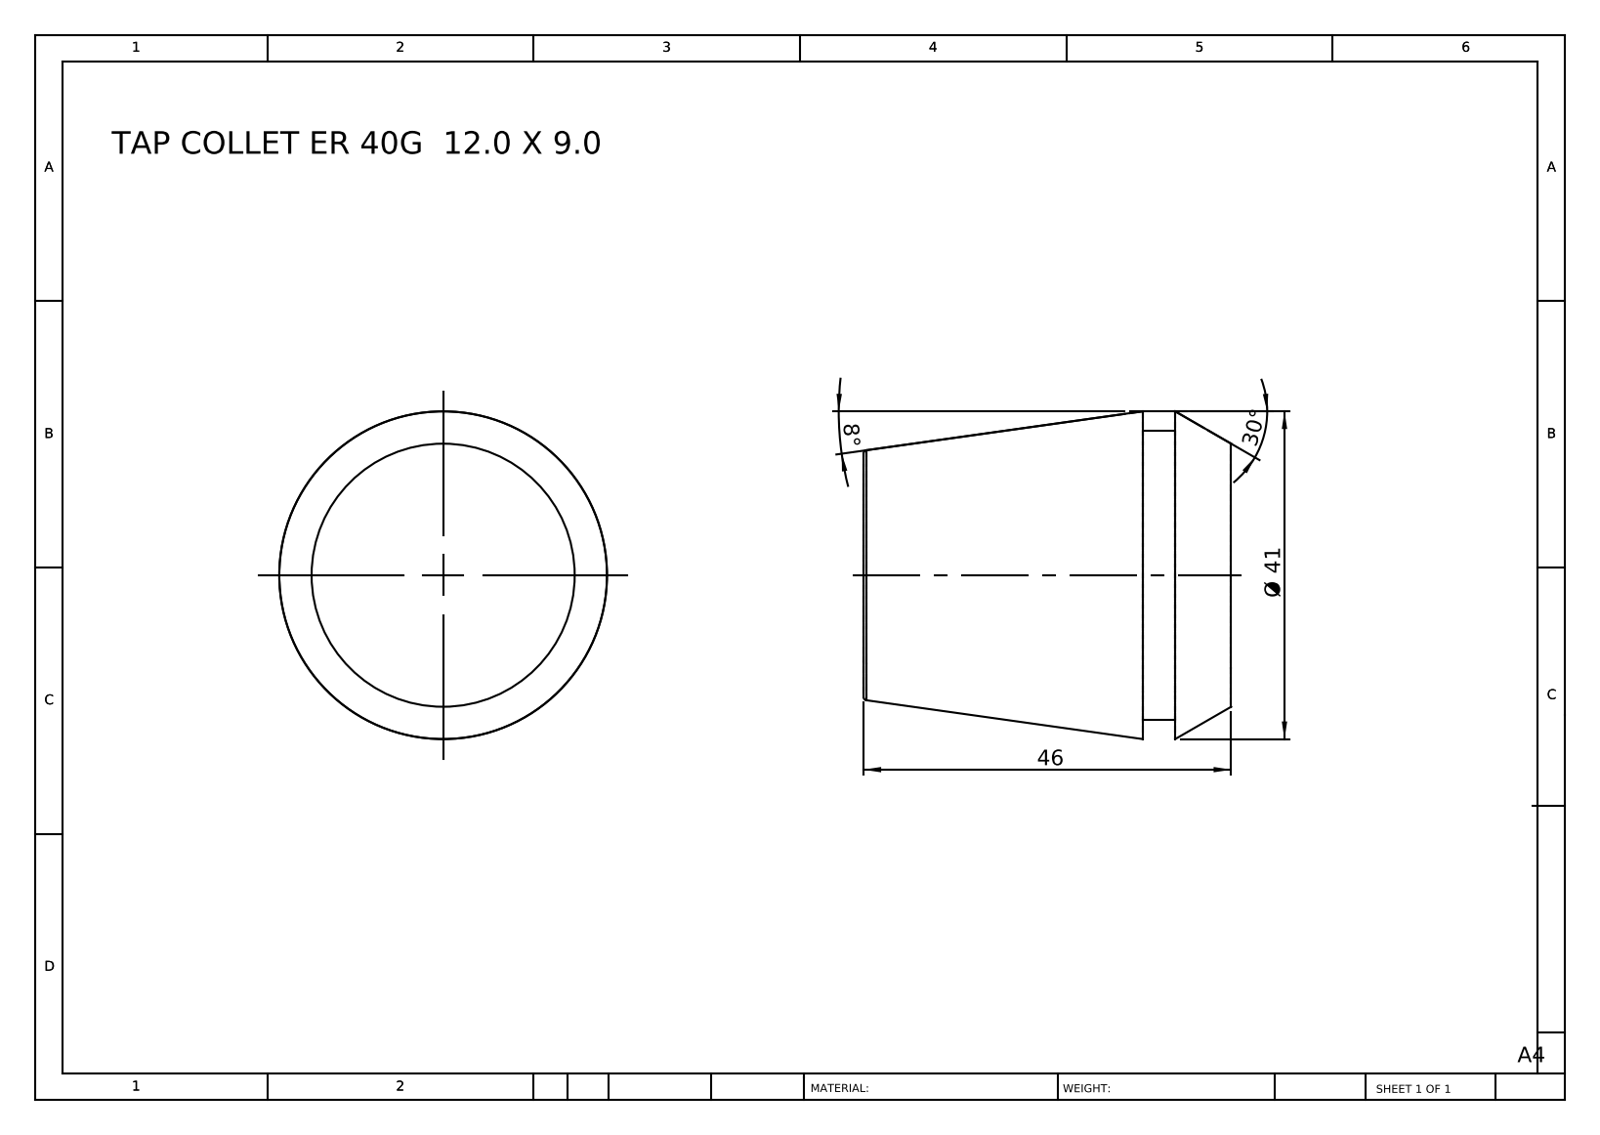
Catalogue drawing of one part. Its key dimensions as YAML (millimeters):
part_name: "TAP COLLET ER 40G 12.0 X 9.0"
step_written_by: "SolidWorks 2014 (CONFIG_CONTROL_DESIGN)"
units: millimeters
bodies: {solids: 1, faces: 12, planar: 4, cylindrical: 2, other: 6}
overall_size: [46, 41, 41]
volume: 47690
surface_area: 7586
round_bosses_or_shafts:
  - {diameter: 36.2, count: 1}
face_to_face_distances: [46, 11.1, 34.9, 7, 4.1, 39]
